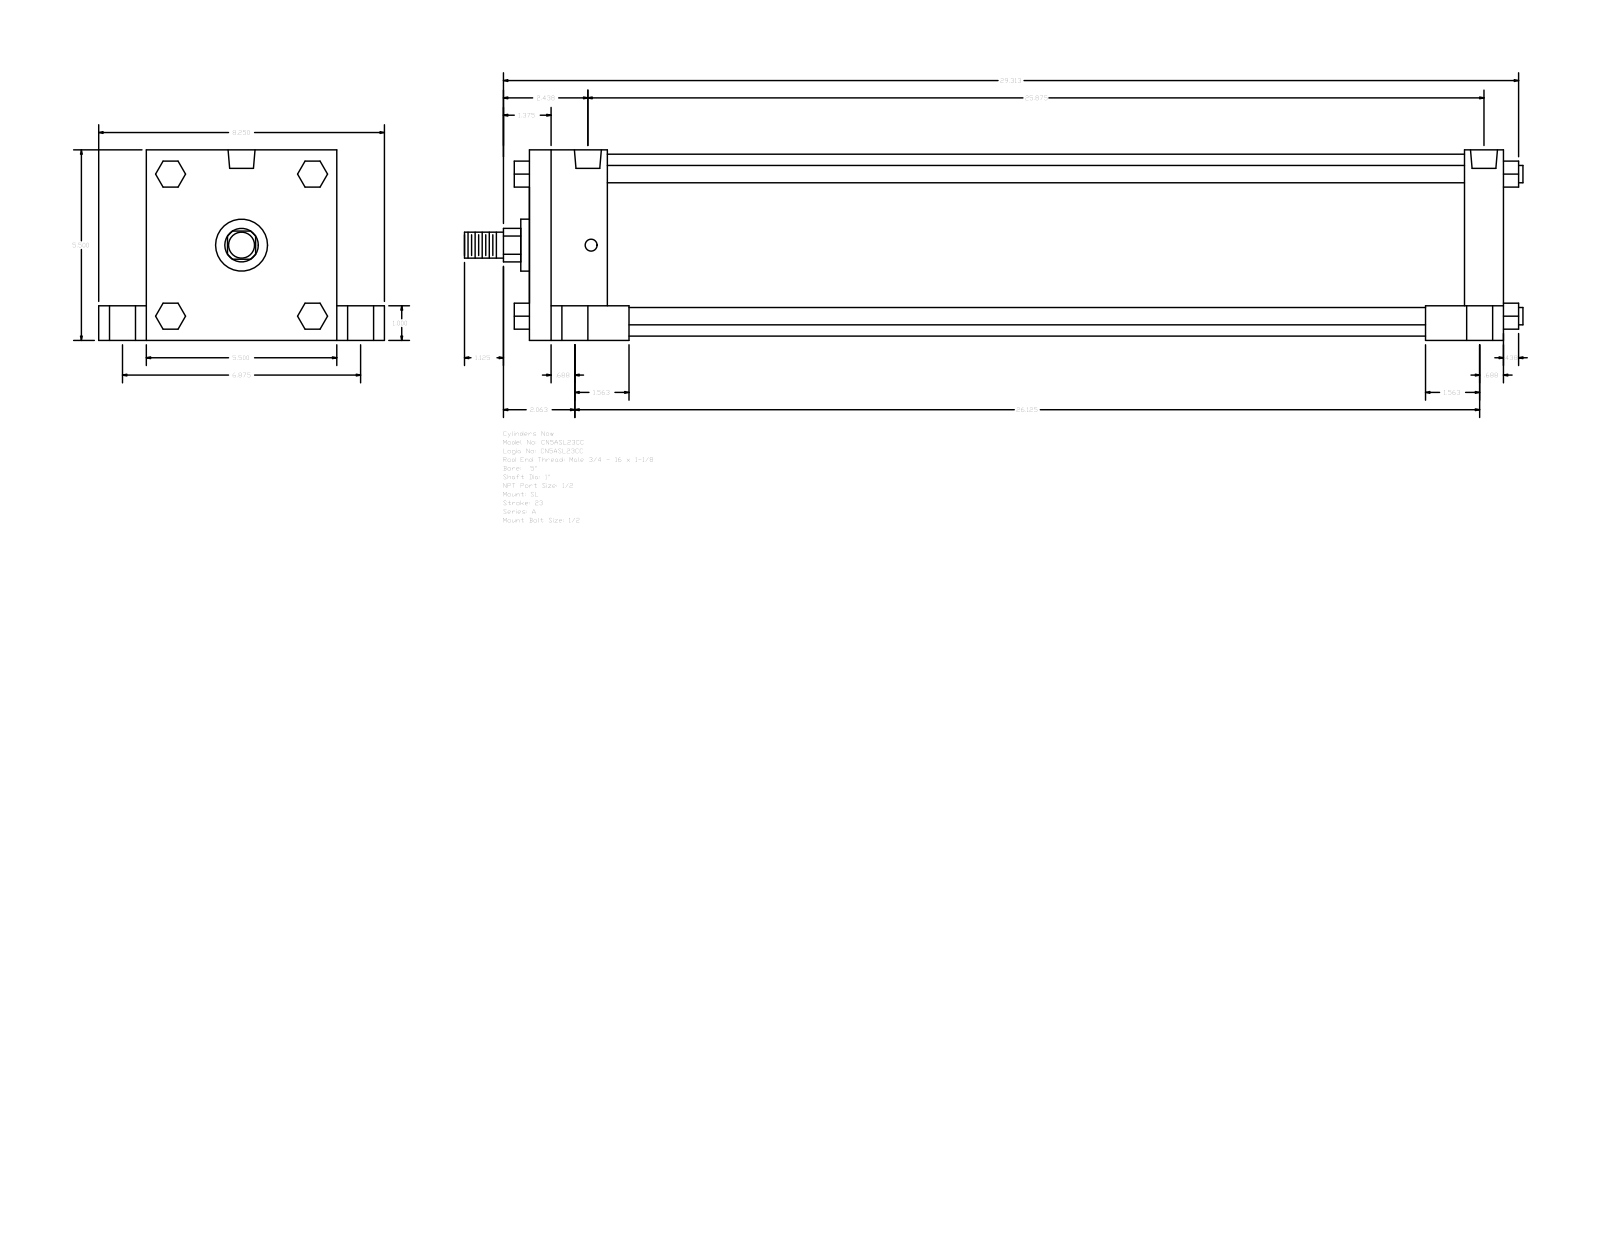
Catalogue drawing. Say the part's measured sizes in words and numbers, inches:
The part is named "A_SL__0500_1". Its 3-D file was written by "GSSL Pune (CONFIG_CONTROL_DESIGN)". It is 0 solids with 150 faces: 114 planar, 36 cylindrical and 0 other. Overall it measures 30.563 by 8.25 by 5.5 inches. Round holes: 4 of diameter 0.344, 4 of diameter 0.75, 4 of diameter 1, 2 of diameter 0.778. Round bosses or shafts: 4 of diameter 0.5, 1 of diameter 5.25, 1 of diameter 1.5, 1 of diameter 1, 1 of diameter 0.75. Partial cylindrical surfaces (rounded edges, fillets, slot ends): 1 of radius 0.484. The main face-to-face distances are 5.5, 28.125, 2.25, 25.875, 1, 4.5, 1.375, 6.875, 1.125, 27. The hole center spacings are 0.094, 3.437, 3.44, 3.458, 3.469, 6.875, 25.687, 25.781.
